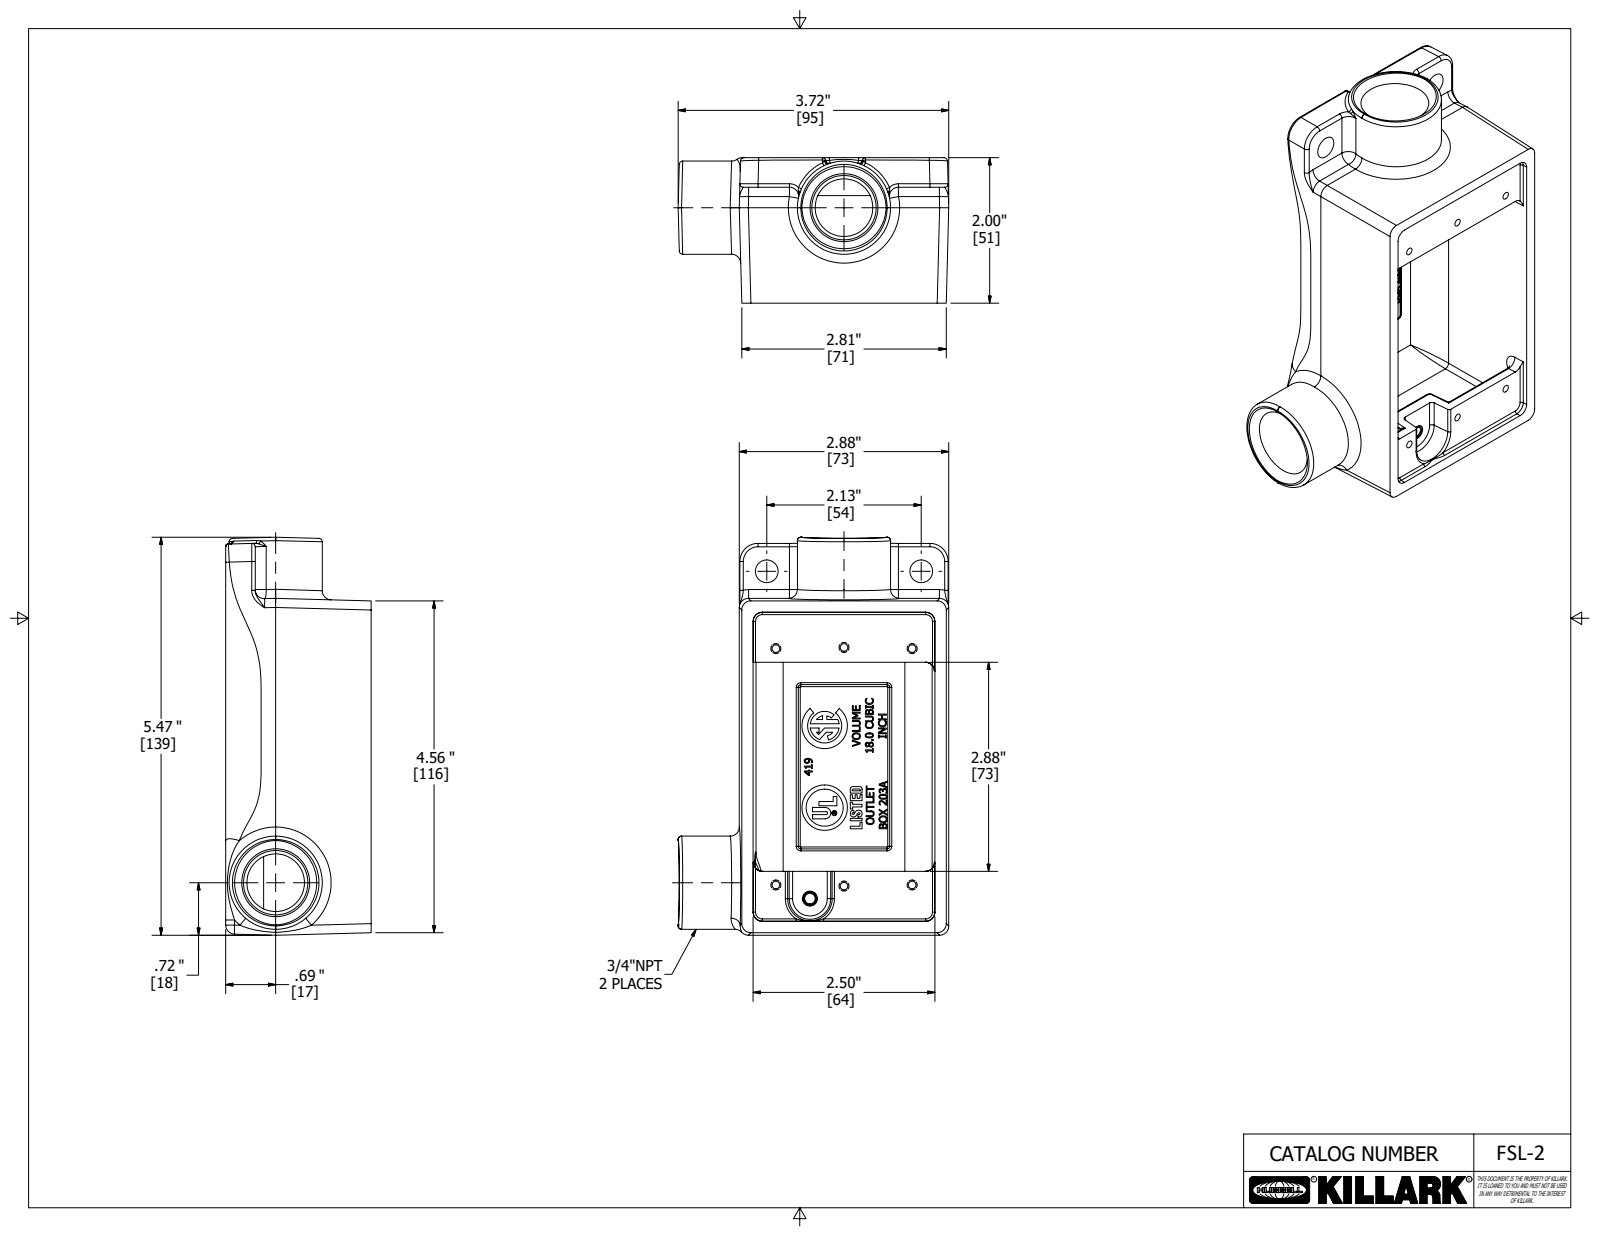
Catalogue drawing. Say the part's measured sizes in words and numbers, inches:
The part is named "23858-3". Its 3-D file was written by "Autodesk Inventor 2020 (AUTOMOTIVE_DESIGN)". It is 1 solid with 1125 faces: 558 planar, 158 cylindrical and 409 other. Overall it measures 5.472 by 3.722 by 2.075 inches. Its volume is 9.193 cubic inches and its surface area 95.75 square inches. Round holes: 6 of diameter 0.104, 2 of diameter 0.792, 1 of diameter 0.069, 1 of diameter 0.145, 1 of diameter 0.625. Round bosses or shafts: 1 of diameter 1.281, 1 of diameter 0.509, 1 of diameter 0.058. Partial cylindrical surfaces (rounded edges, fillets, slot ends): 30 of radius 0.031, 18 of radius 0.125, 14 of radius 0.047, 7 of radius 0.094, 5 of radius 0.062, 4 of radius 0.375, 2 of radius 0.013, 2 of radius 0.014. The main face-to-face distances are 2.656, 0.156, 4.406, 1.75, 0.225, 0.031, 1.719, 1.594, 1.906, 0.25. The hole center spacings are 0.937, 3.397, 1.875, 3.25, 3.752, 0.153, 0.5, 0.505.
